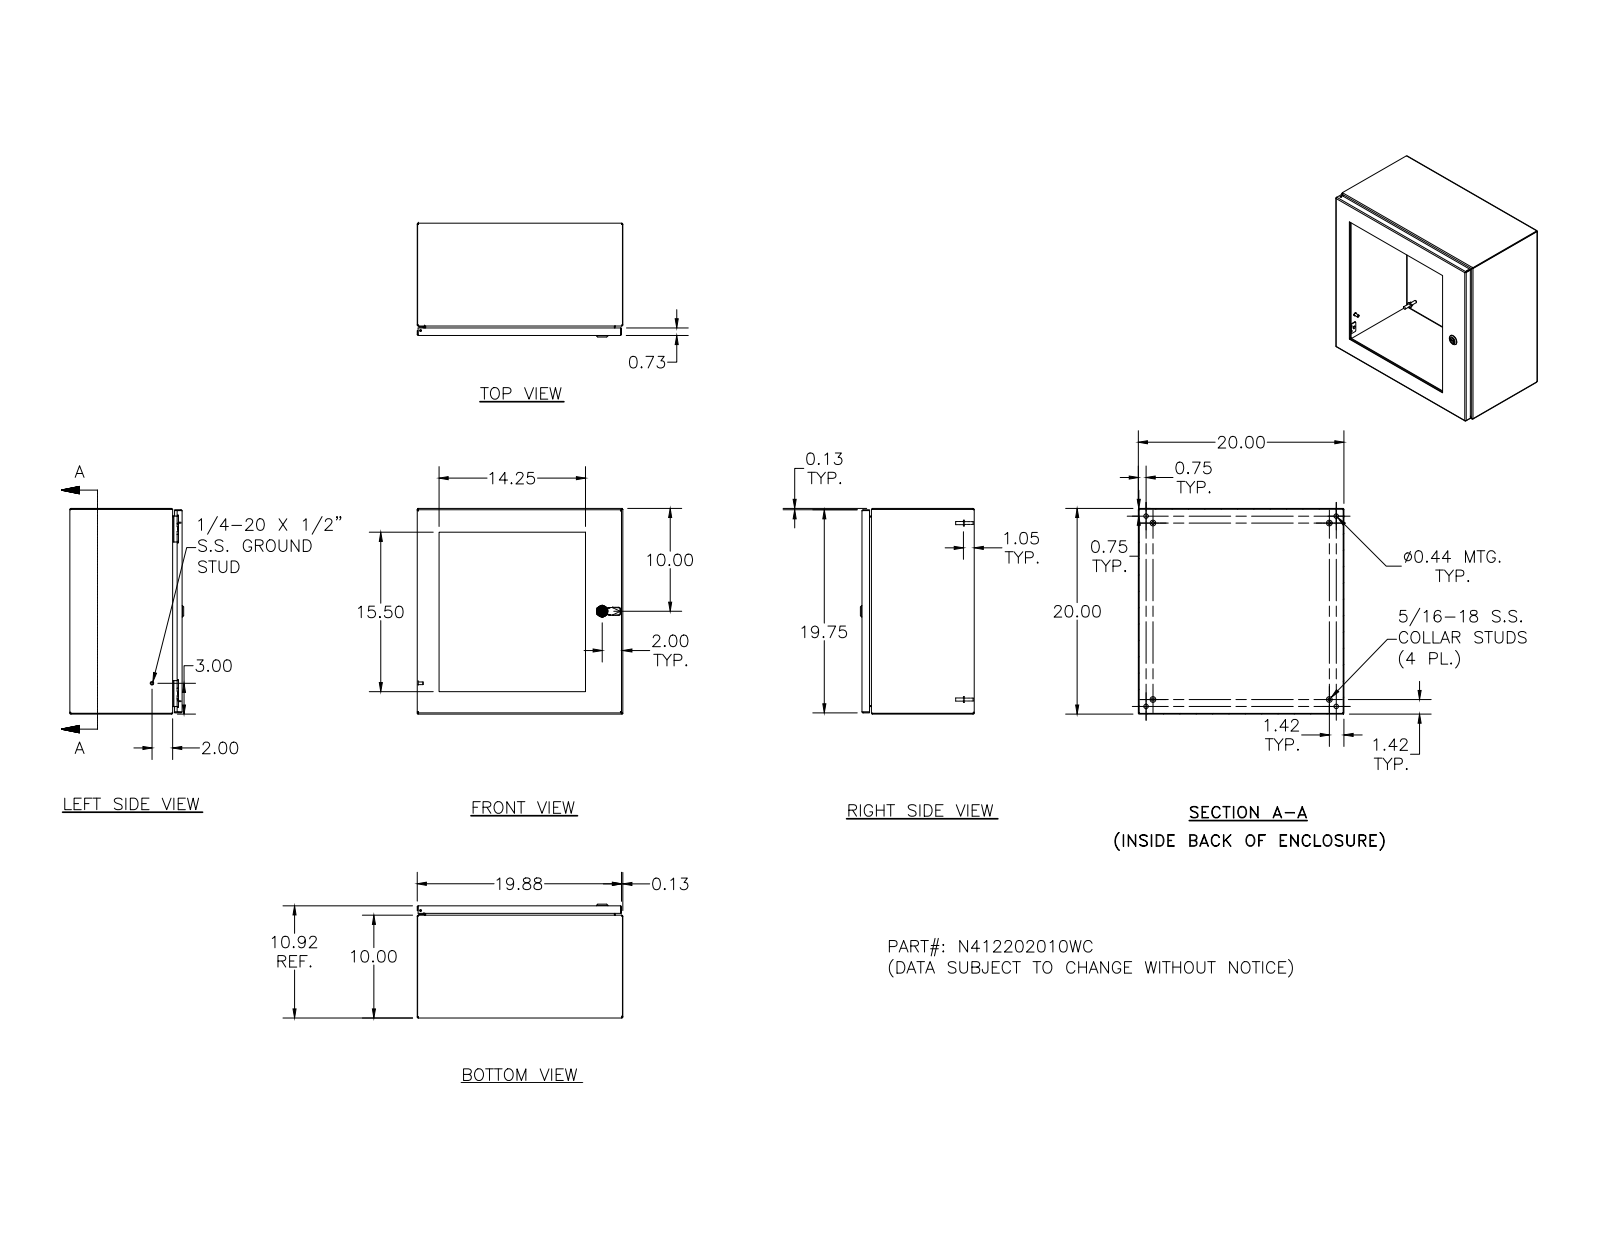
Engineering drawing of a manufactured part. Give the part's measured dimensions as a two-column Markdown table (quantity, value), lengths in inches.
| quantity | value |
| --- | --- |
| part name | N412202010WC |
| STEP written by | SolidWorks 2018 (AUTOMOTIVE_DESIGN) |
| units | inches |
| bodies | 69 solids, 2019 faces (753 planar, 617 cylindrical, 649 other) |
| overall size | 20 × 20 × 11.075 |
| volume | 182.3 in³ |
| surface area | 3 784 in² |
| round holes (diameter × count) | 0.156 × 18, 0.281 × 16, 0.188 × 5, 0.093 × 4, 0.152 × 4, 0.167 × 4, 0.172 × 4, 0.437 × 4, 0.187 × 1, 0.197 × 1, 0.315 × 1, 0.394 × 1 |
| round bosses / shafts (diameter × count) | 0.337 × 16, 0.19 × 16, 0.25 × 10, 0.563 × 4, 0.36 × 4, 0.32 × 4, 0.3 × 4, 0.275 × 4 |
| partial cylindrical surfaces (radius × count) | 0.031 × 34, 0.012 × 30, 0.05 × 26, 0.105 × 24, 0.016 × 18, 0.125 × 16, 0.02 × 13, 0.032 × 8 |
| main face-to-face distances | 0.074, 19.926, 10.843, 10.769, 20, 19.852, 0.25, 10.593, 10.519, 10.917 |
| hole center spacings | 4, 8, 16.008, 16, 17.221, 6.221, 8.585, 10.035 |
